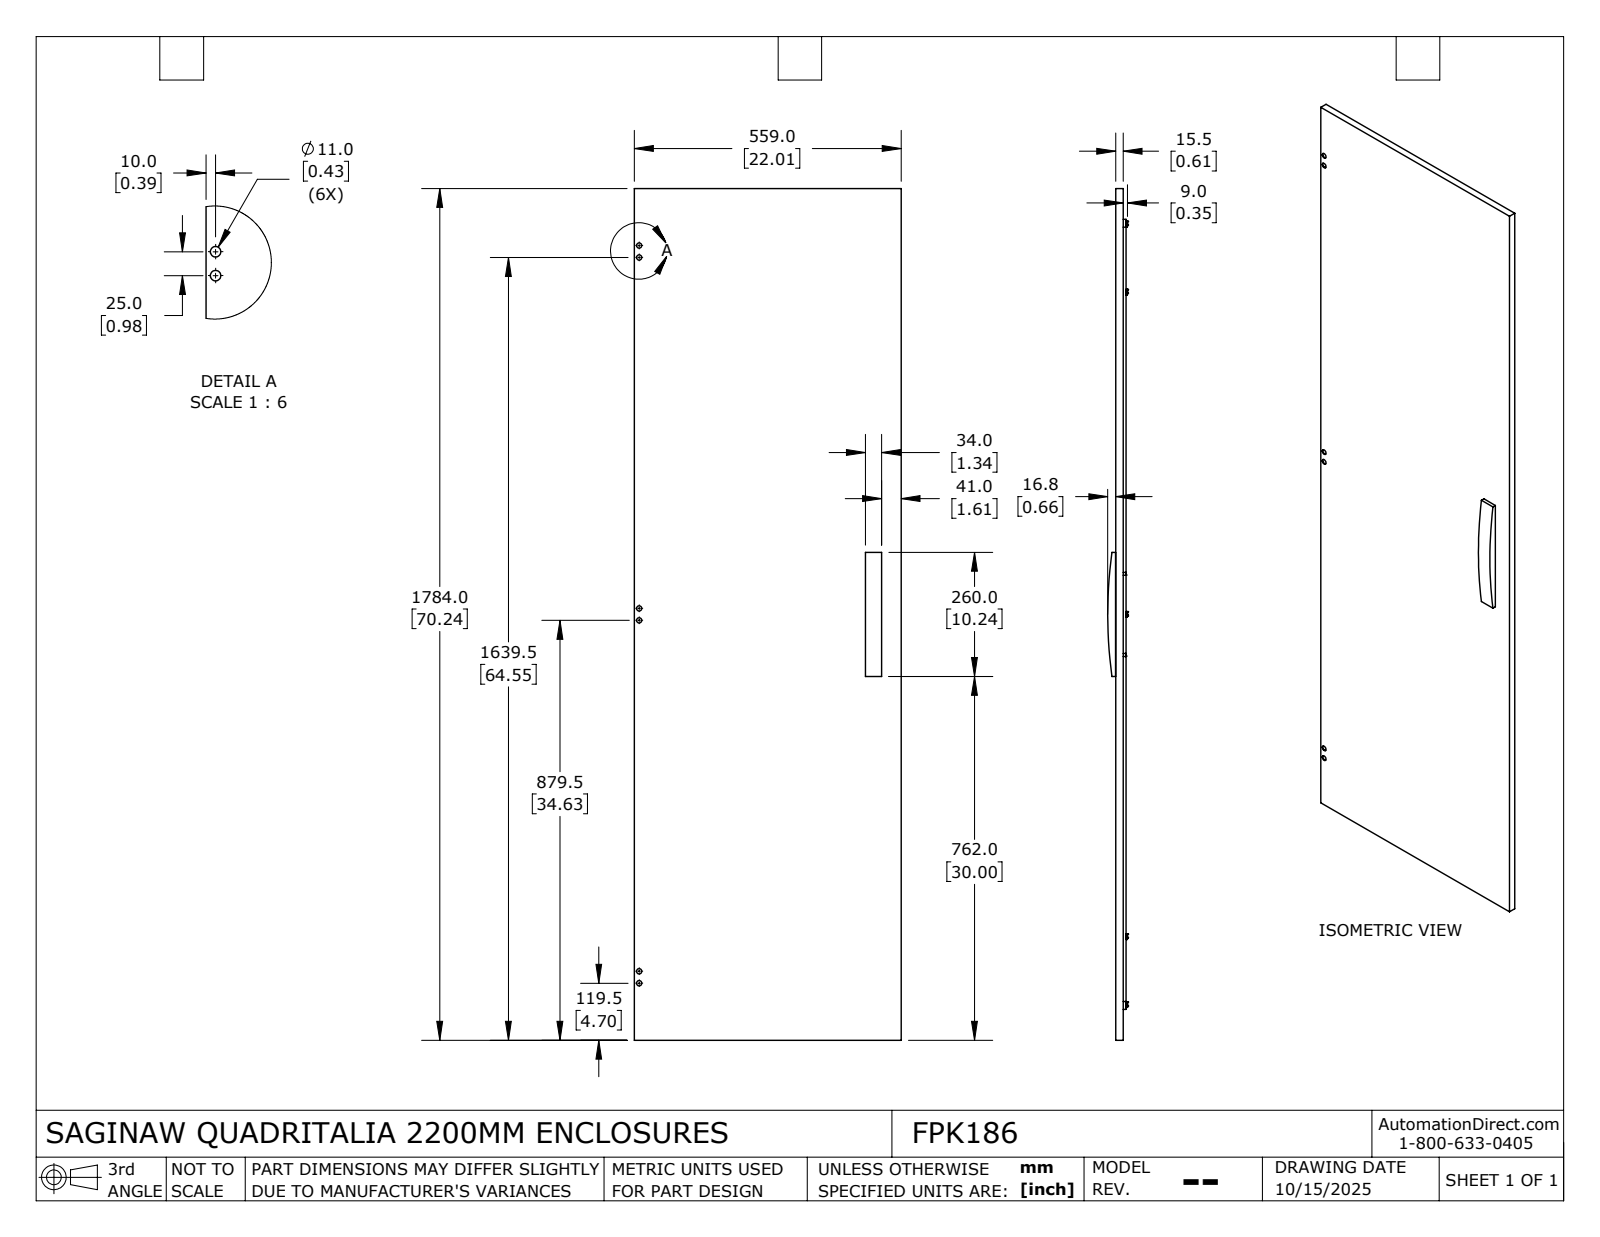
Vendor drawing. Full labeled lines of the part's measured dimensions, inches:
Part name (STEP PRODUCT): FPK186
STEP written by: SolidWorks 2024 (AUTOMOTIVE_DESIGN)
Units: inches
Bodies: 2 solids, 550 faces (263 planar, 187 cylindrical, 100 other)
Overall size (bounding box): 70.236 × 22.008 × 1.627
Volume: 223.1 in³ · Surface area: 3 650 in²
Round holes (diameter × count): ⌀0.167 ×120, ⌀0.194 ×8, ⌀0.354 ×8, ⌀0.433 ×6
Round bosses / shafts (diameter × count): ⌀0.276 ×4, ⌀0.236 ×4
Partial cylindrical surfaces — rounded edges, fillets, slot ends (radius × count): R0.227 ×8, R0.296 ×4, R37.908 ×1
Main face-to-face distances: 0.059, 0.787, 0.846, 14.173, 21.949, 14.961, 13.386, 2.953, 19.055, 2.894
Hole centre spacings: 0.984, 1.969, 2.953, 3.937, 4.921, 5.906, 8.858, 6.89
